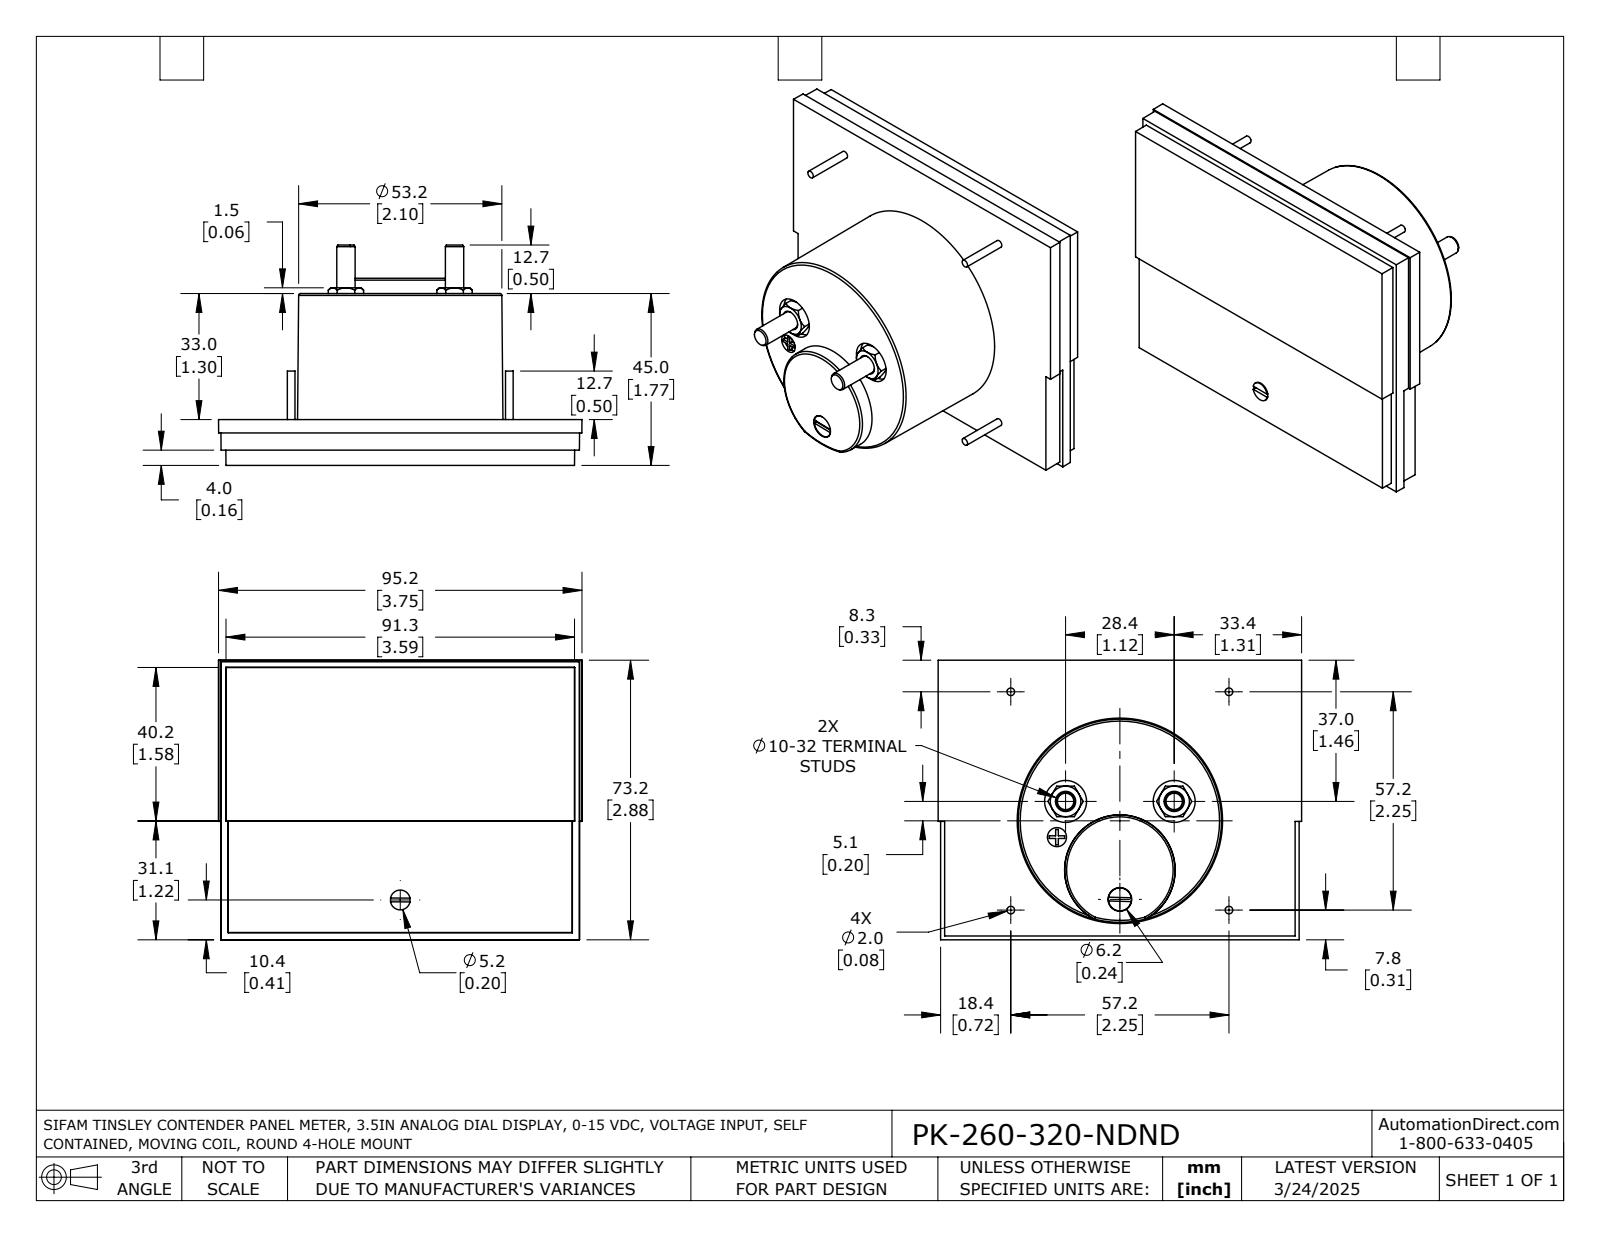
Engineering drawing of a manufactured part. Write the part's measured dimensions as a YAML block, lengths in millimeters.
part_name: "PK-260-320-NDND"
step_written_by: "SolidWorks 2021 (AUTOMOTIVE_DESIGN)"
units: millimeters
bodies: {solids: 1, faces: 163, planar: 76, cylindrical: 31, other: 56}
overall_size: [95.2, 73.2, 57.7]
volume: 154800
surface_area: 24770
round_holes:
  - {diameter: 11, count: 2}
  - {diameter: 5, count: 1}
  - {diameter: 6.2, count: 1}
round_bosses_or_shafts:
  - {diameter: 2, count: 4}
  - {diameter: 4.8, count: 2}
  - {diameter: 6, count: 1}
  - {diameter: 5.2, count: 1}
partial_cylinders:
  - {radius: 2.5, count: 1}
face_to_face_distances: [12, 0.8, 11.3, 45, 33, 44.2, 4, 1.9, 8, 37]
hole_center_spacings: [29.3, 9.6, 23.2, 28.4, 32.1]
